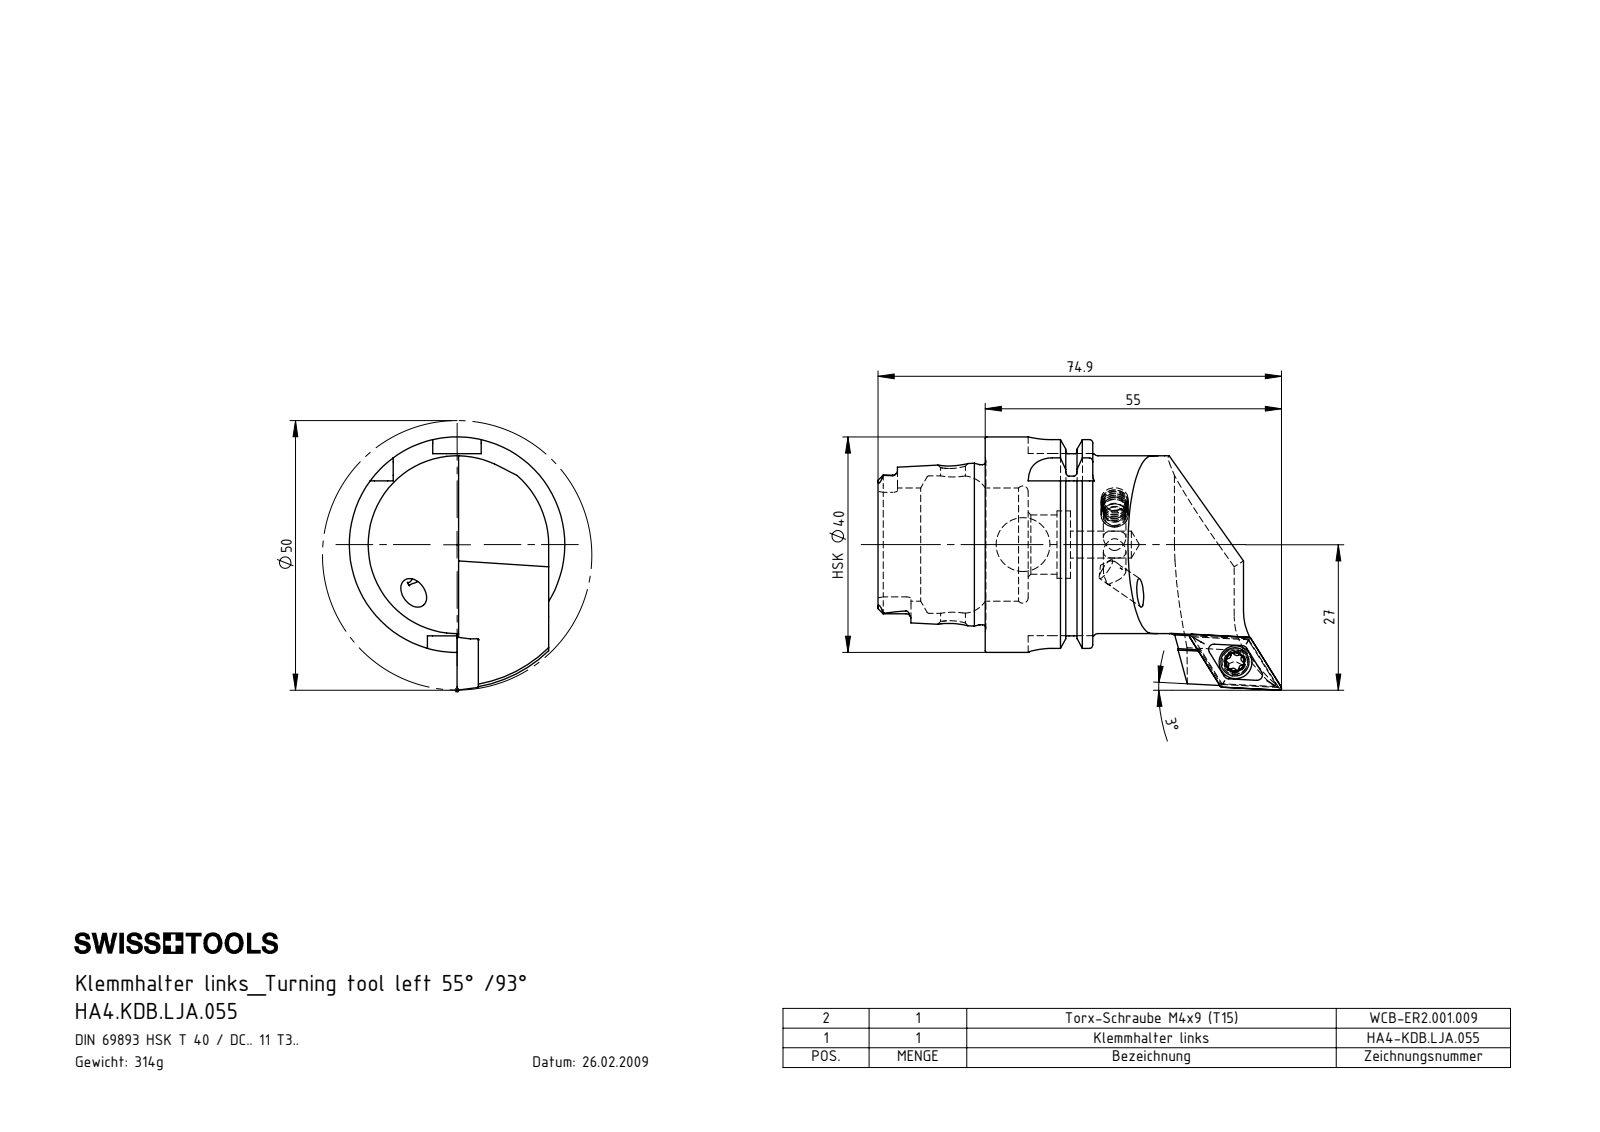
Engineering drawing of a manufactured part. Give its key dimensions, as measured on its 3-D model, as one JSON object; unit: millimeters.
{"part_name": "HA4-KDB.LJA.055; KVT_MB_600_050; DCMT11T304; WCB-ER2.001.009_A (+1 more)", "step_written_by": "SolidWorks 2011 (CONFIG_CONTROL_DESIGN)", "units": "millimeters", "bodies": {"solids": 5, "faces": 313, "planar": 79, "cylindrical": 89, "other": 145}, "overall_size": [74.91, 47, 40], "volume_mm3": 40320, "surface_area_mm2": 13729, "round_holes": [[4.2, 2], [3.3, 1], [4, 1], [4.4, 1], [4.6, 1], [5, 1], [6.1, 1], [10, 1], [11, 1], [12.5, 1], [21, 1], [25.5, 1]], "round_bosses_or_shafts": [[40, 1], [34.75, 1], [33, 1], [29.71, 1], [5.25, 1], [5, 1], [4, 1]], "partial_cylinders_radius": [[0.34, 6], [0.59, 6], [0.9, 6], [4.5, 4], [1.82, 2], [1.88, 2], [4, 1], [18, 1]], "face_to_face_distances": [17.7, 48, 7.95, 40.05, 19.95, 12, 28.05, 14.03, 3.67, 19.9], "hole_center_spacings": [44.96, 45.08]}
